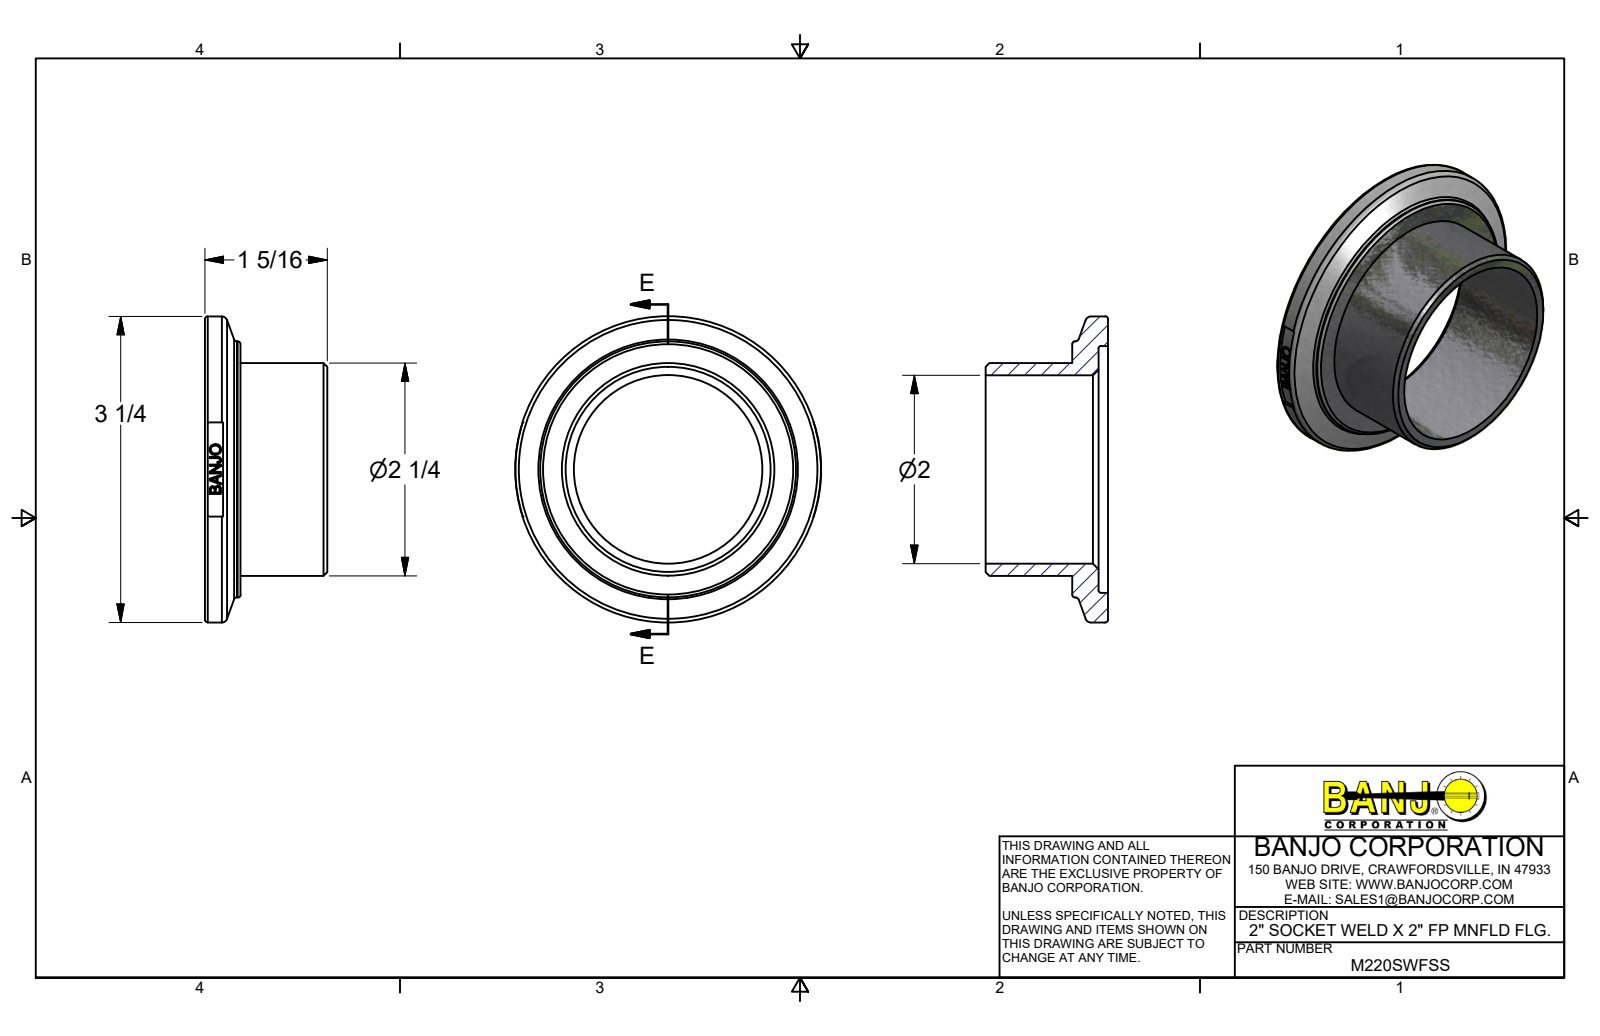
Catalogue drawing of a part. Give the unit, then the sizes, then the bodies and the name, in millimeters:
Units: millimetres
Overall size (bounding box): 82.55 × 82.55 × 33.02
Round holes (diameter × count): ⌀50.8 ×1, ⌀66.55 ×1
Round bosses / shafts (diameter × count): ⌀82.55 ×1, ⌀69.06 ×1, ⌀57.4 ×1
Partial cylindrical surfaces — rounded edges, fillets, slot ends (radius × count): R39.75 ×1, R40.51 ×1
Main face-to-face distances: 2.54, 7.08, 9.62, 23.4, 30.48, 33.02, 1.78, 32.26, 8.86, 0.76
Volume: 36 402 mm³ · Surface area: 17 850 mm²
Bodies: 1 solid, 255 faces (108 planar, 27 cylindrical, 120 other)
Part name (STEP PRODUCT): M220SWFSS
STEP written by: Autodesk Inventor 2017 (AUTOMOTIVE_DESIGN)
